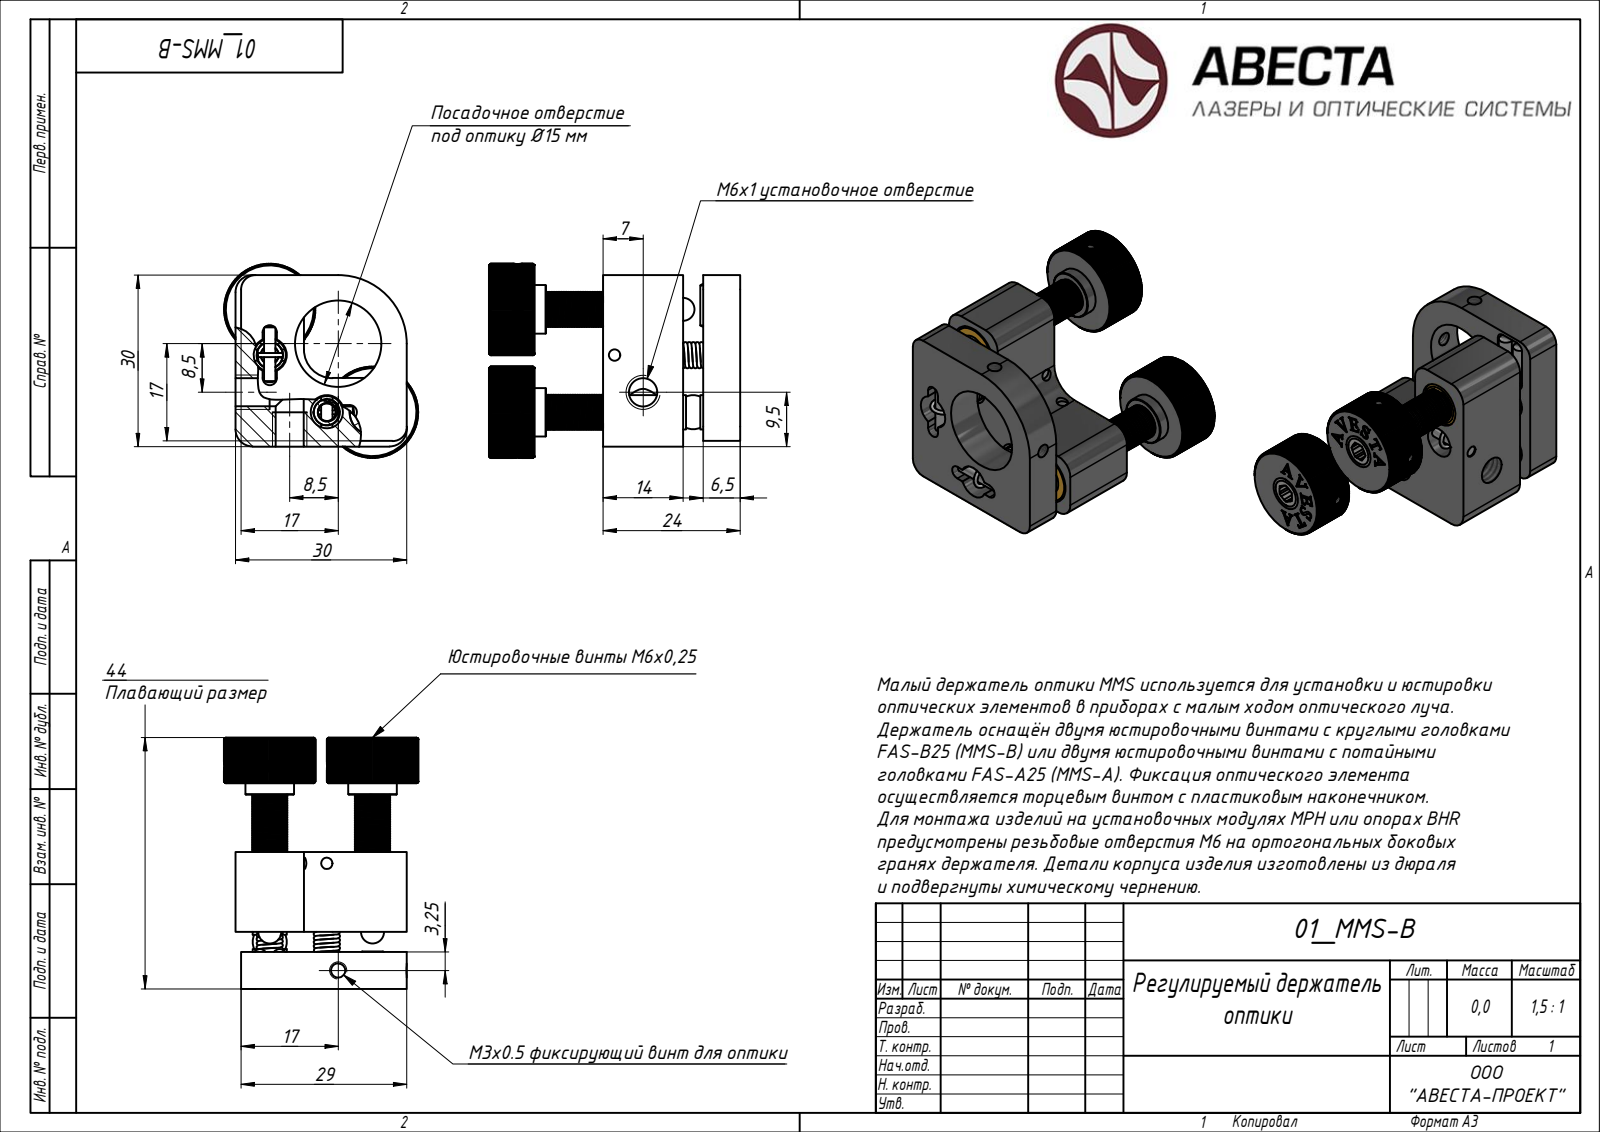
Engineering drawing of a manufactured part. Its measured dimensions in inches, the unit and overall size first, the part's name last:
Units: inches
Overall size (bounding box): 1.598 × 1.339 × 1.339
Main face-to-face distances: 0.256, 0.138, 0.394, 0.945, 0.689, 0.551, 0.039, 0.472, 1.181, 0.433
Volume: 0.891 in³ · Surface area: 19.31 in²
Bodies: 22 solids, 647 faces (278 planar, 0 cylindrical, 369 other)
STEP written by: ST-DEVELOPER v15 (AUTOMOTIVE_DESIGN)
